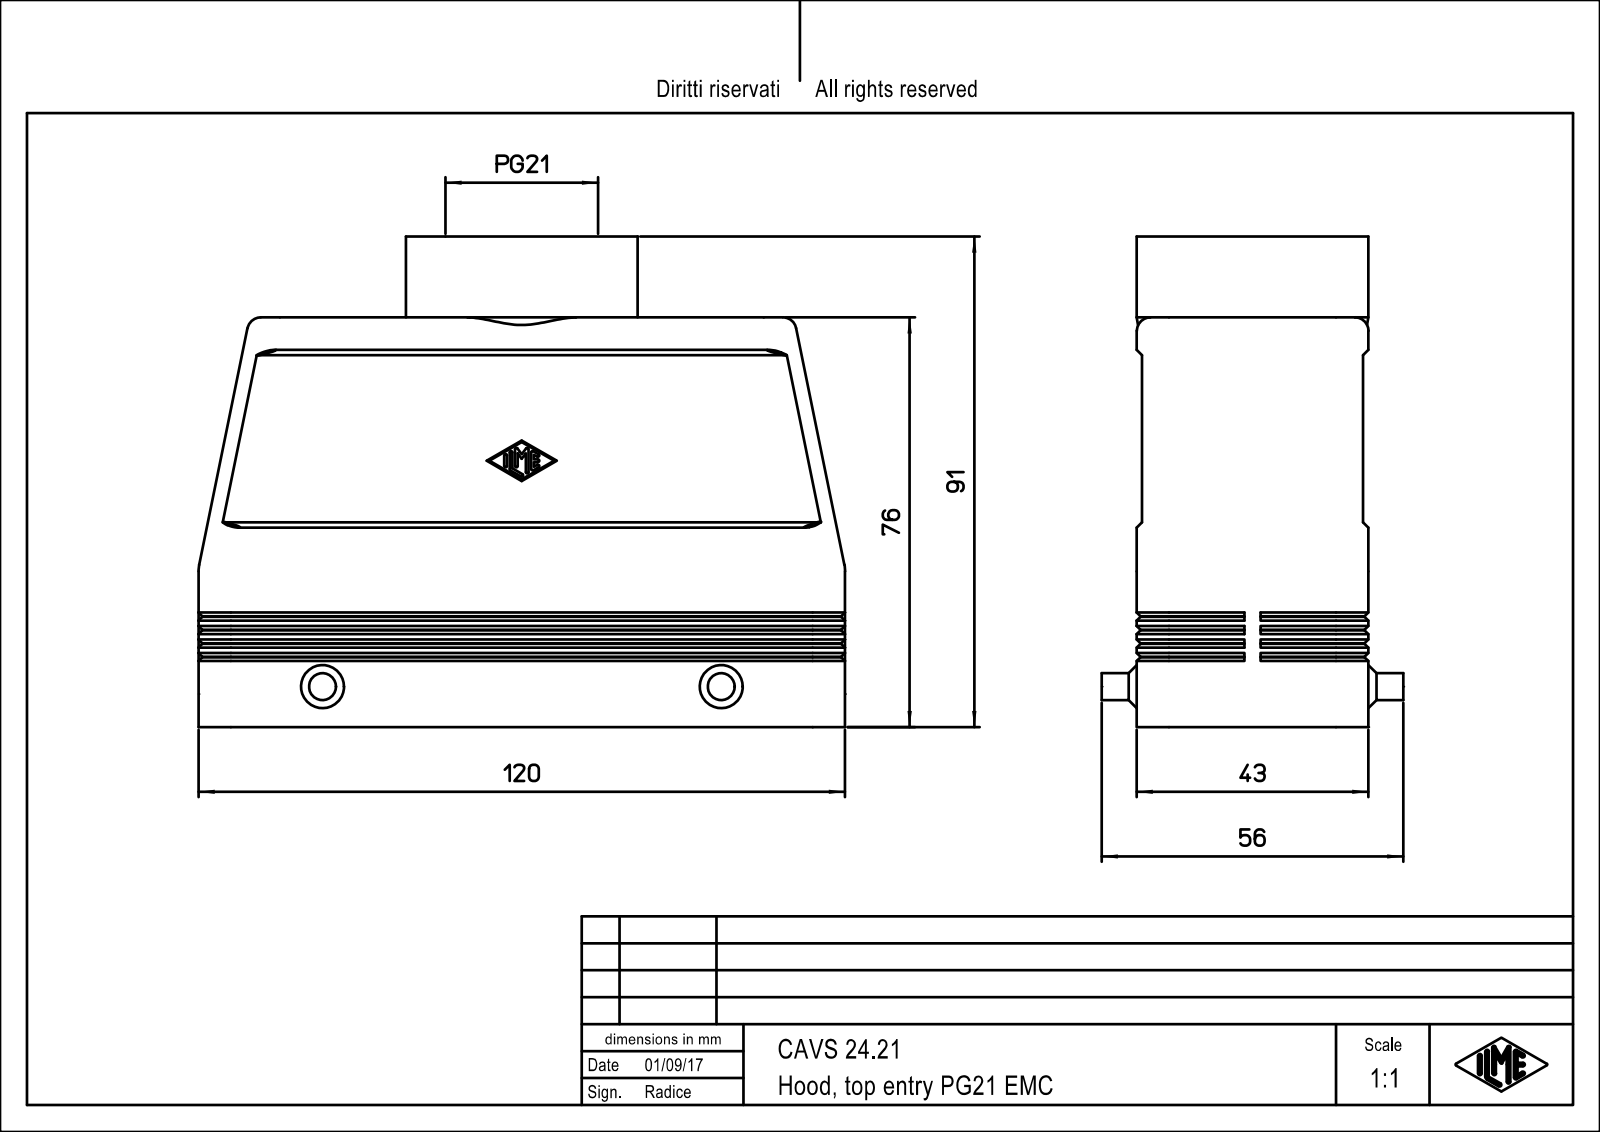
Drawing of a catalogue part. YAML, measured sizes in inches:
part_name: "CAVS_24.21"
step_written_by: "PTC Creo Elements/Direct Modeling 19.0E 27-Jun-2016 (C) Parametric Technology GmbH (AUTOMOTIVE_DESIGN)"
units: inches
bodies: {solids: 1, faces: 339, planar: 179, cylindrical: 98, other: 62}
overall_size: [4.724, 3.583, 2.205]
volume: 5.865
surface_area: 88.34
round_holes:
  - {diameter: 0.097, count: 4}
  - {diameter: 0.157, count: 4}
  - {diameter: 0.965, count: 1}
  - {diameter: 1.114, count: 1}
round_bosses_or_shafts:
  - {diameter: 0.197, count: 2}
  - {diameter: 1.693, count: 1}
partial_cylinders:
  - {radius: 0.01, count: 14}
  - {radius: 0.236, count: 10}
  - {radius: 0.079, count: 4}
  - {radius: 0.098, count: 4}
  - {radius: 0.118, count: 4}
  - {radius: 0.209, count: 4}
face_to_face_distances: [0.118, 1.457, 1.575, 0.079, 0.039, 1.654, 1.535, 1.693, 1.614, 0.472]
hole_center_spacings: [2.115, 1.063, 4.094, 4.23]
